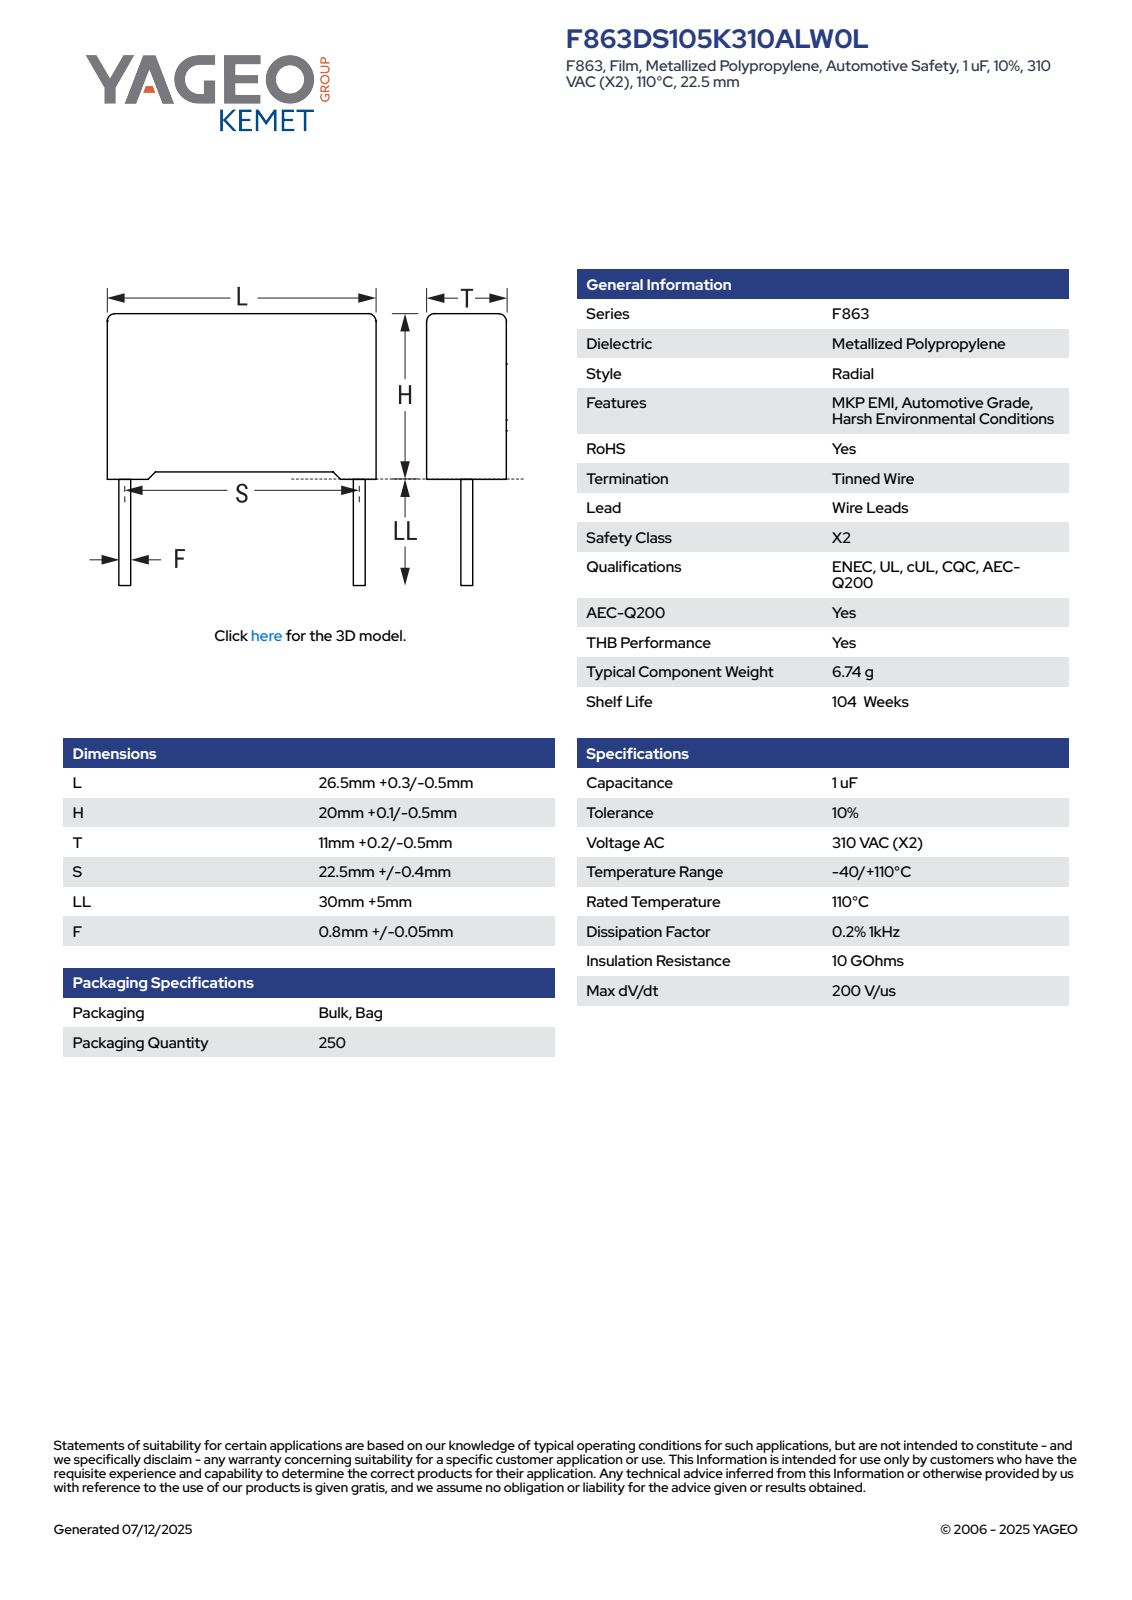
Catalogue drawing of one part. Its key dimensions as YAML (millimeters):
part_name: "CFR_RB_26.5X20X11_L26.8H20.1T11.2S22.5LL35F0.85"
step_written_by: "SolidWorks 2014 (AUTOMOTIVE_DESIGN)"
units: millimeters
bodies: {solids: 4, faces: 89, planar: 81, cylindrical: 8, other: 0}
overall_size: [55.1, 26.8, 11.21]
volume: 5802
surface_area: 2308
round_bosses_or_shafts:
  - {diameter: 0.85, count: 2}
partial_cylinders:
  - {radius: 0.72, count: 4}
face_to_face_distances: [11.2, 19.2, 26.8, 11.21, 10.6, 0.6, 0.9, 20.1, 10.61, 0.61]
